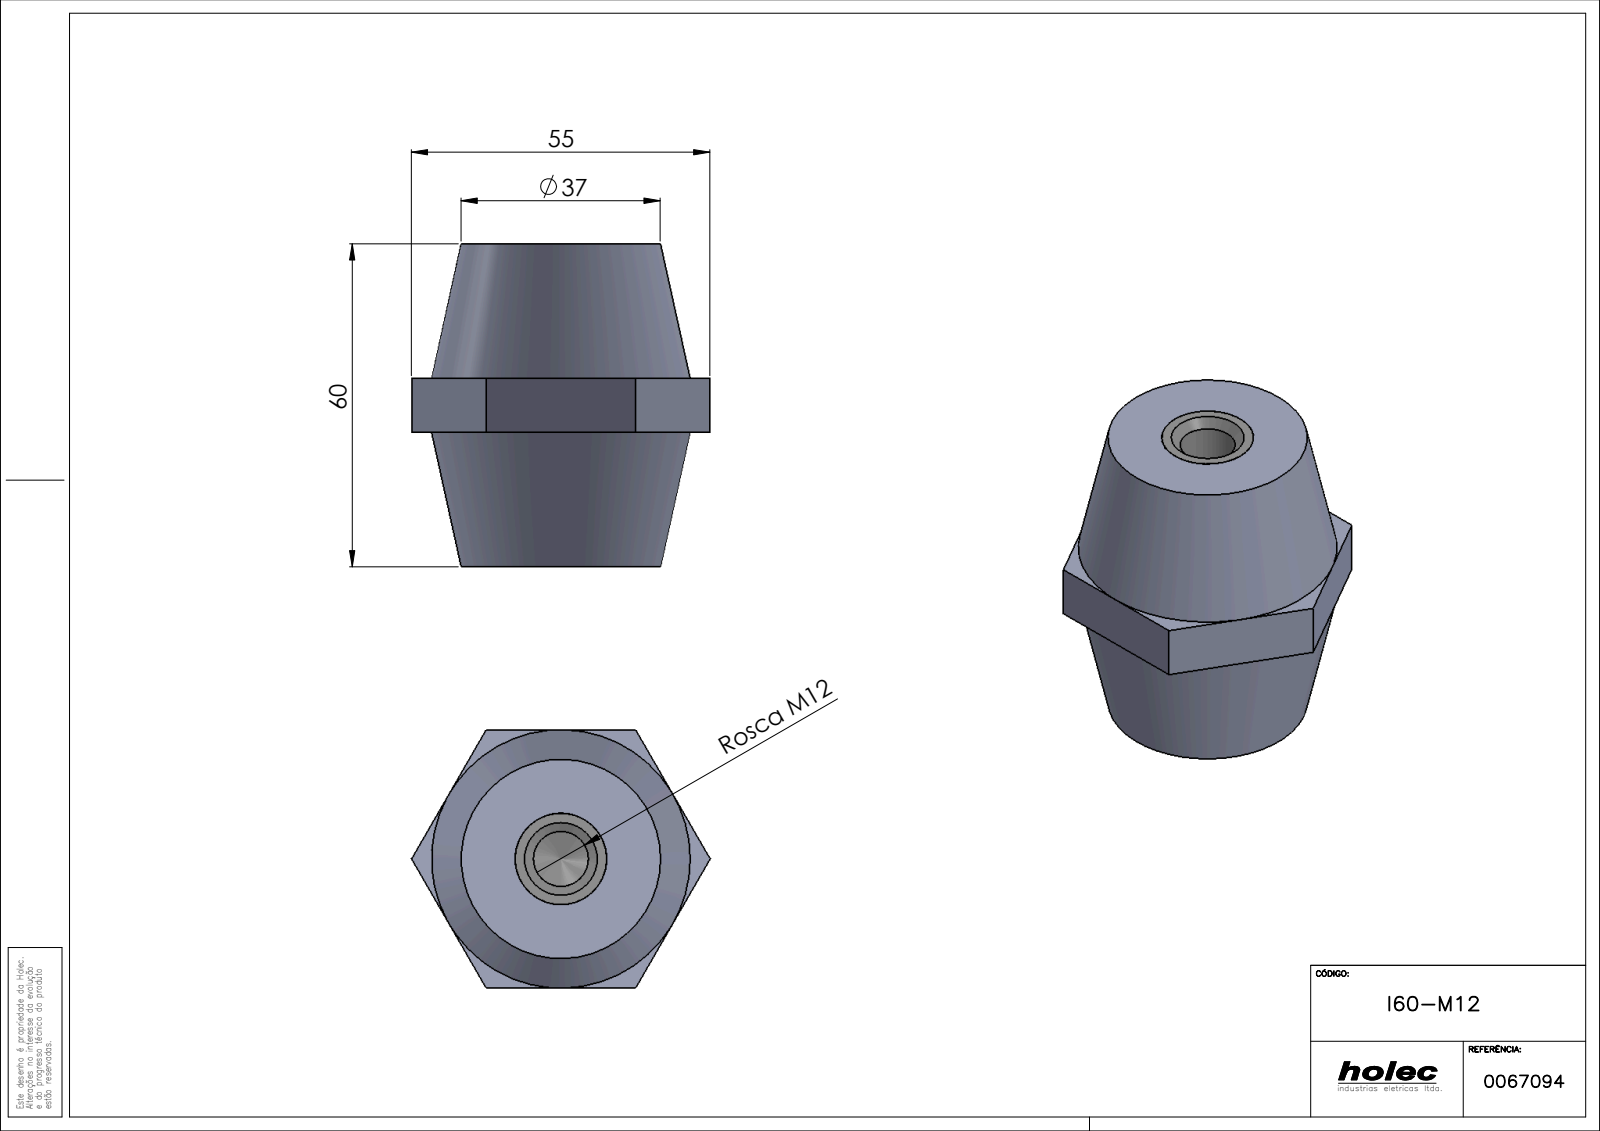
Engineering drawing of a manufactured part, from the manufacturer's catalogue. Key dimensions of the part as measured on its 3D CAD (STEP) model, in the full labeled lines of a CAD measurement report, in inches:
Part name (STEP PRODUCT): PB1_0003; I60-M12; PB1_0108(PB1_0109_12)
STEP written by: SolidWorks 2017 (AUTOMOTIVE_DESIGN)
Units: inches
Bodies: 3 solids, 162 faces (82 planar, 12 cylindrical, 68 other)
Overall size (bounding box): 2.362 × 2.182 × 1.89
Volume: 5.405 in³ · Surface area: 27.4 in²
Round holes (diameter × count): ⌀0.402 ×1, ⌀0.551 ×1
Main face-to-face distances: 0.669, 2.362, 1.614, 1.89, 0.748, 0.531, 0.217, 1.615, 0.315, 0.984
